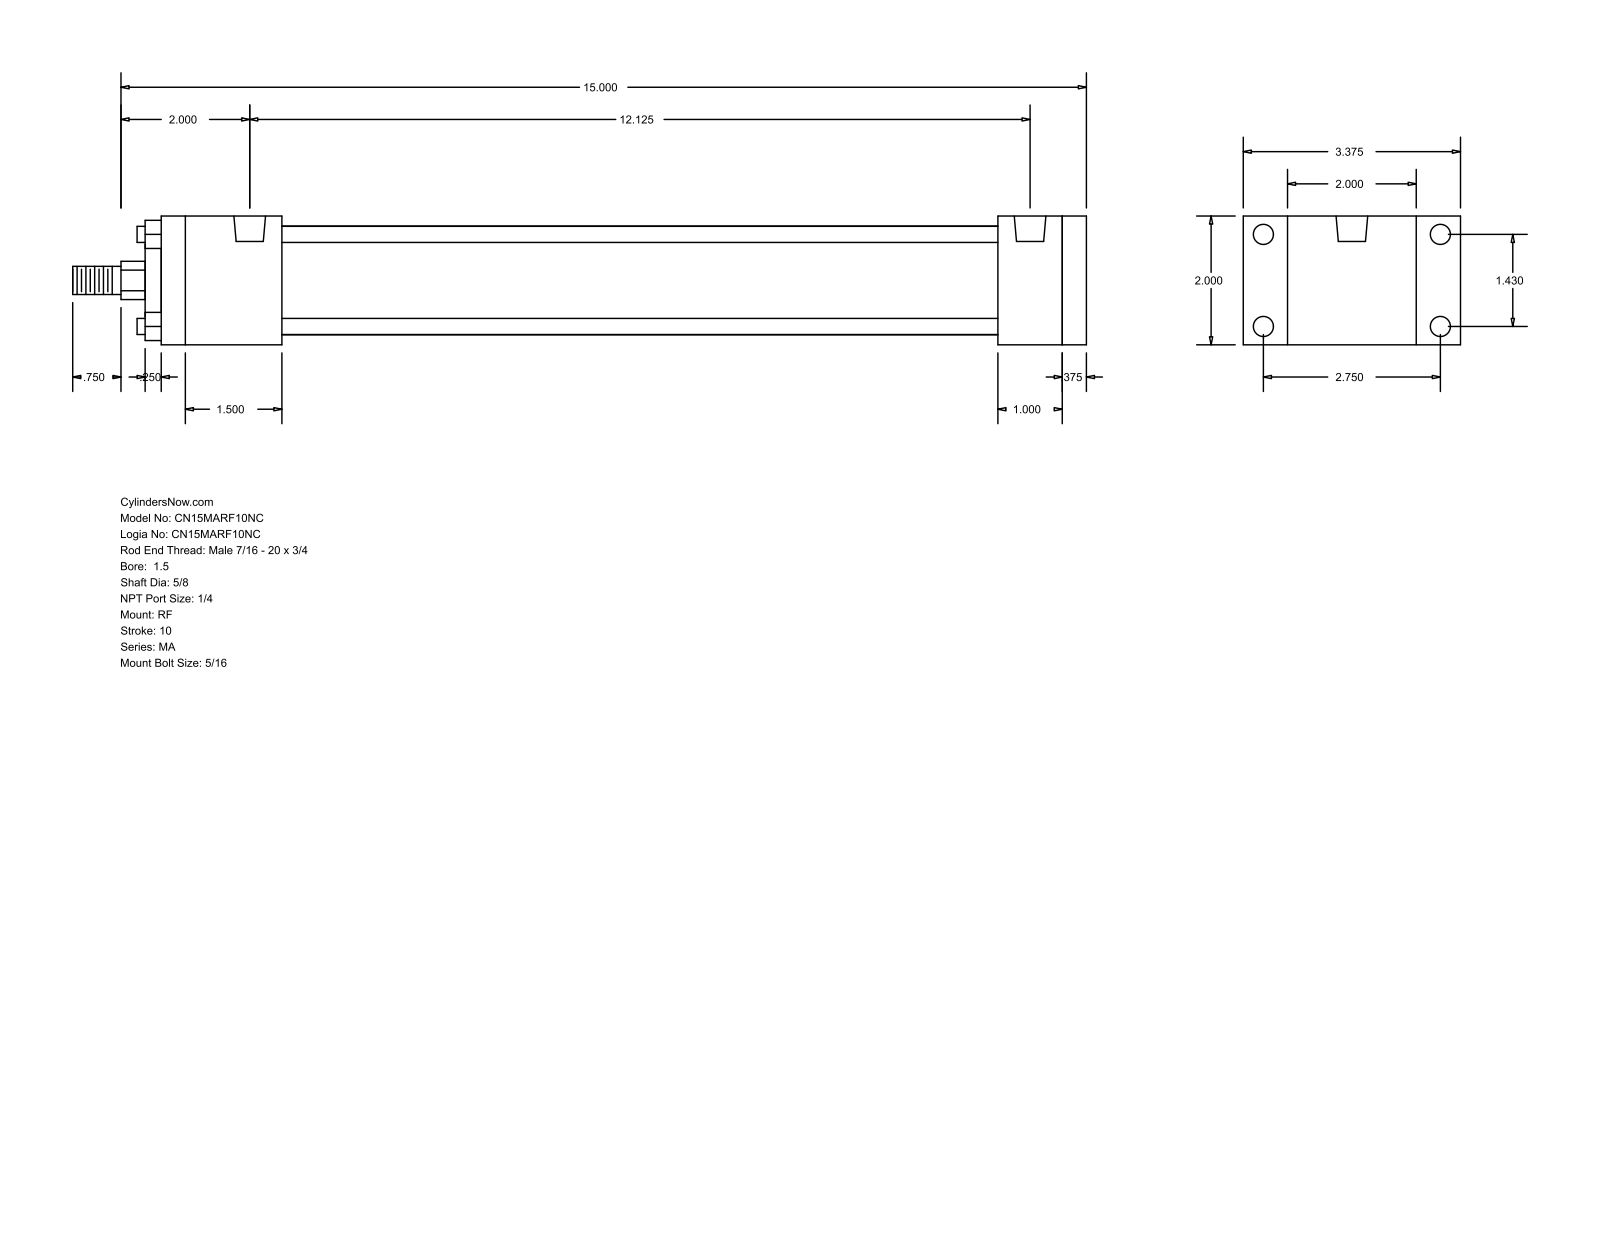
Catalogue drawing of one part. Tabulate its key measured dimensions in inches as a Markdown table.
| quantity | value |
| --- | --- |
| part name | MA_RF__0150_0.625 |
| STEP written by | GSSL Pune (CONFIG_CONTROL_DESIGN) |
| units | inches |
| bodies | 0 solids, 92 faces (64 planar, 28 cylindrical, 0 other) |
| overall size | 15.75 × 3.375 × 2 |
| round holes (diameter × count) | 0.313 × 8, 0.492 × 2 |
| round bosses / shafts (diameter × count) | 0.25 × 4, 1.69 × 1, 1.125 × 1, 0.625 × 1, 0.437 × 1 |
| partial cylindrical surfaces (radius × count) | 0.297 × 1 |
| main face-to-face distances | 2, 14.375, 0.375, 14, 1.375, 13, 1, 1.875, 11.125, 12.125 |
| hole center spacings | 1.43, 2.75, 3.099, 12.125 |
